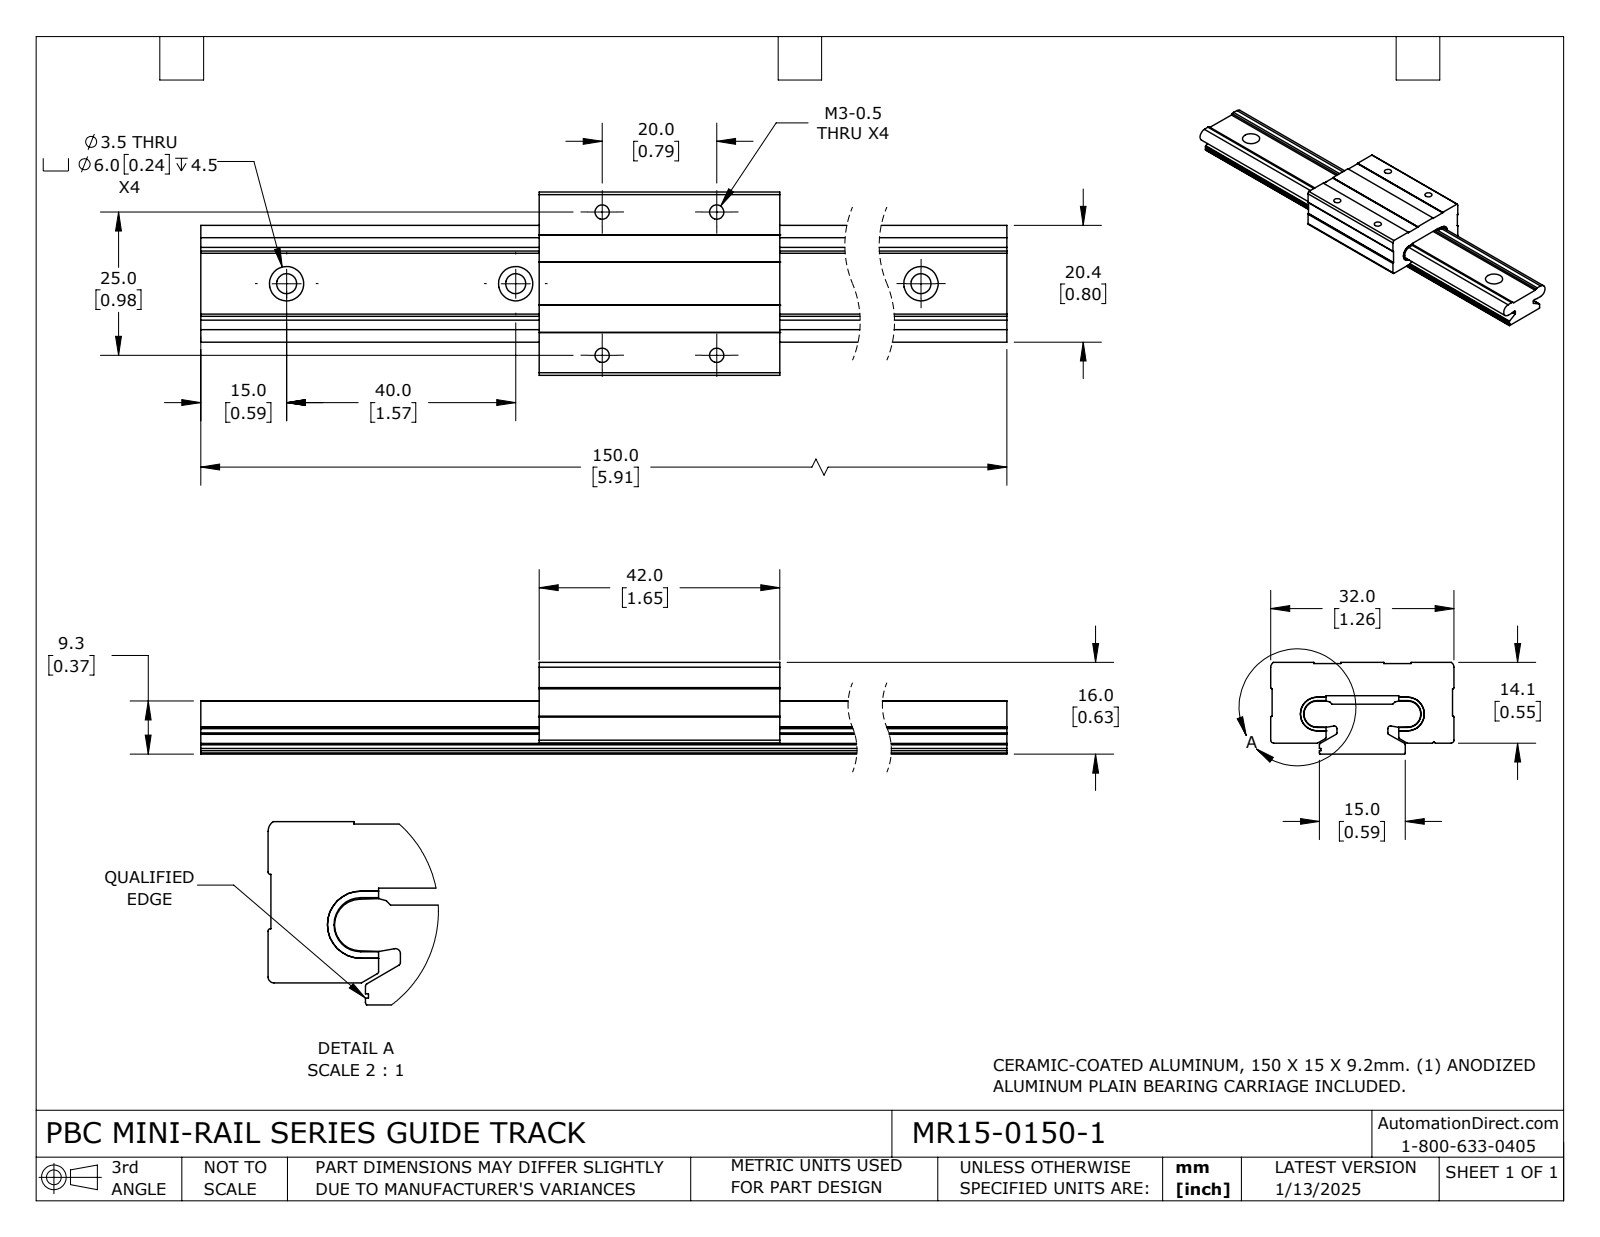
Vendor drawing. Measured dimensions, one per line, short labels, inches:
name: MR15-0150-1_CARRIAGE; MR15-0150-1_RAIL; MR15-0150-1
written by: SolidWorks 2023 (CONFIG_CONTROL_DESIGN)
unit: in
bodies: 4 solids, 148 faces (87 planar, 61 cylindrical, 0 other)
size: 5.906 × 1.26 × 0.63
volume: 2.009 in³; area: 28.95 in²
holes: 4× ⌀0.098, 4× ⌀0.138, 4× ⌀0.236
rounds: 12× R0.008, 6× R0.01, 4× R0.092, 2× R0.018, 2× R0.02, 2× R0.04, 2× R0.089, 2× R0.116
face distances: 0.343, 0.63, 0.287, 0.076, 0.268, 0.554, 0.401, 0.326, 0.058, 0.229
hole spacings: 1.575, 0.529, 0.772, 0.787, 0.984, 1.097, 1.261, 1.467
